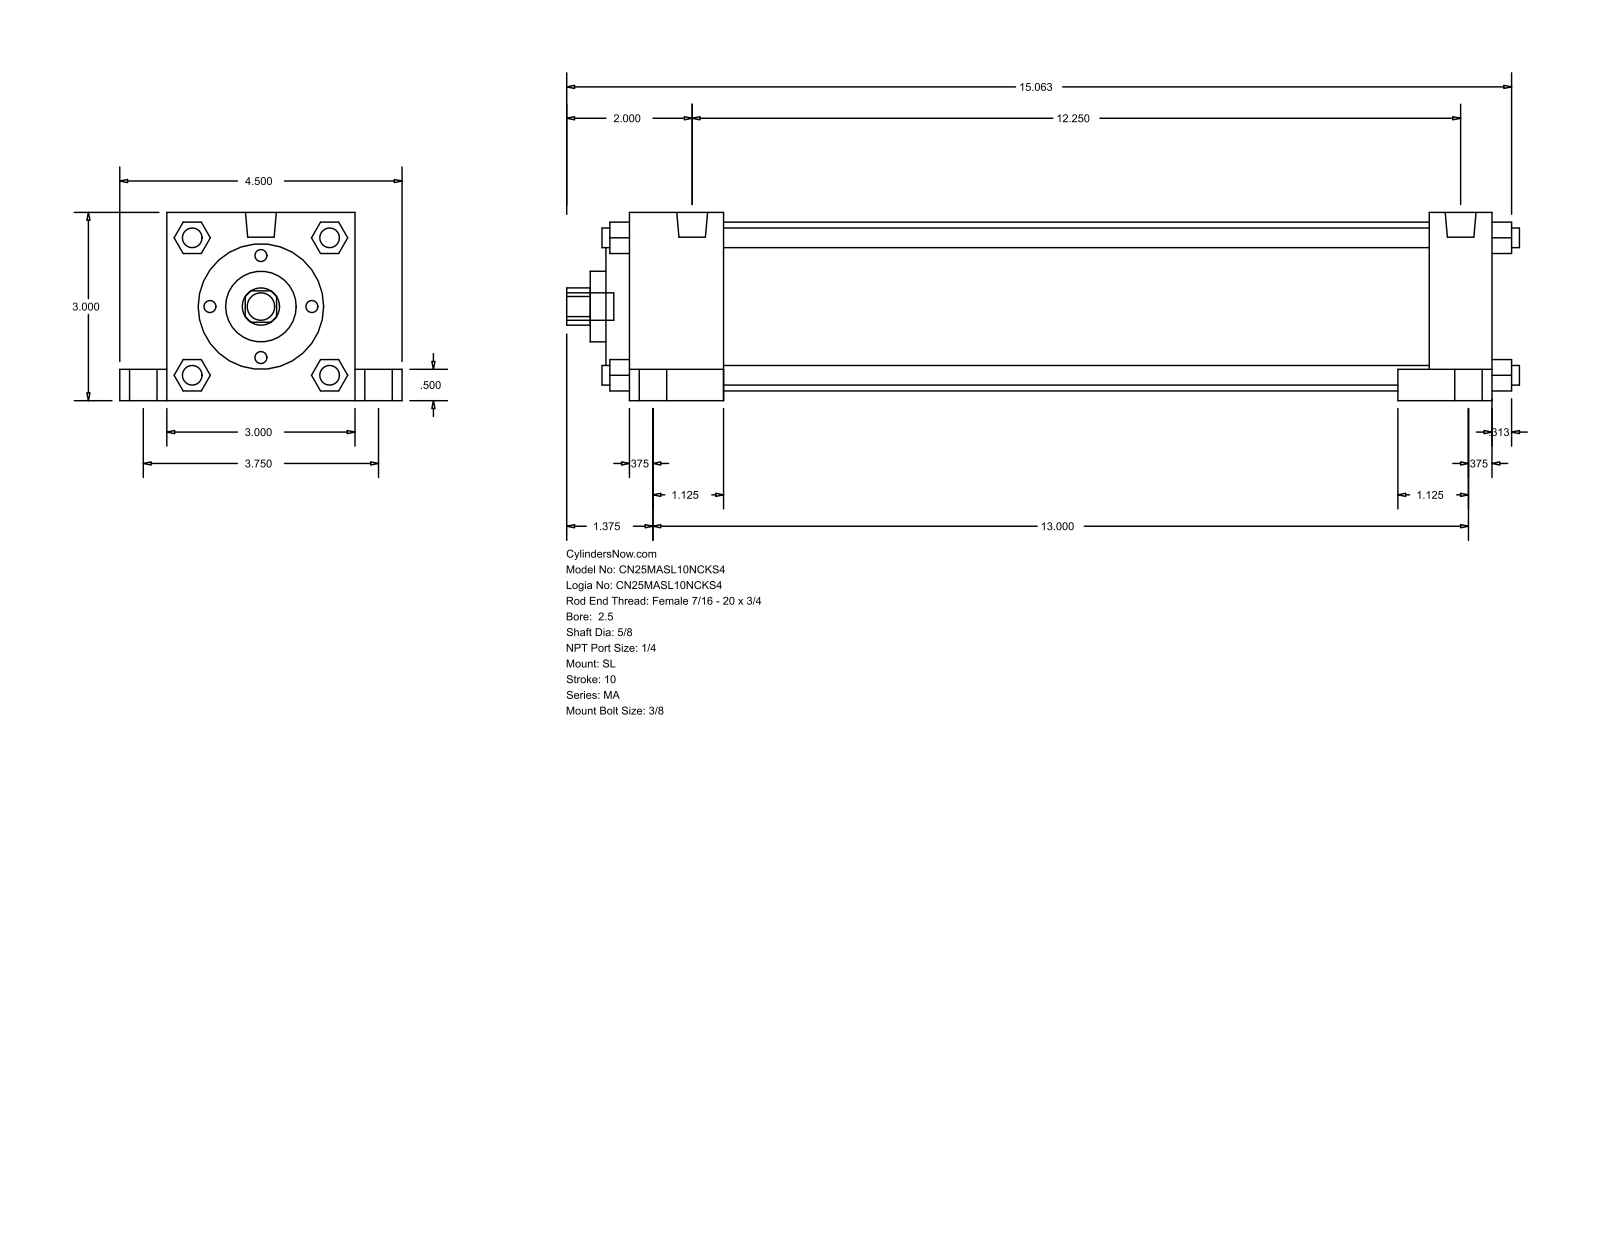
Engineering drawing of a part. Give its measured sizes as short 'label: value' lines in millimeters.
name: MA_SL__0250_0.625
written by: GSSL Pune (CONFIG_CONTROL_DESIGN)
unit: mm
bodies: 0 solids, 150 faces (113 planar, 37 cylindrical, 0 other)
size: 385.76 × 114.3 × 76.2
holes: 1× ⌀15.88, 1× ⌀28.57, 1× ⌀50.8, 1× ⌀68.33
bosses: 8× ⌀7.94, 5× ⌀11.11, 4× ⌀17.46, 2× ⌀12.49
rounds: 1× R7.54
face distances: 76.2, 349.25, 12.7, 285.75, 25.4, 38.1, 311.15, 323.85, 19.05, 63.5
